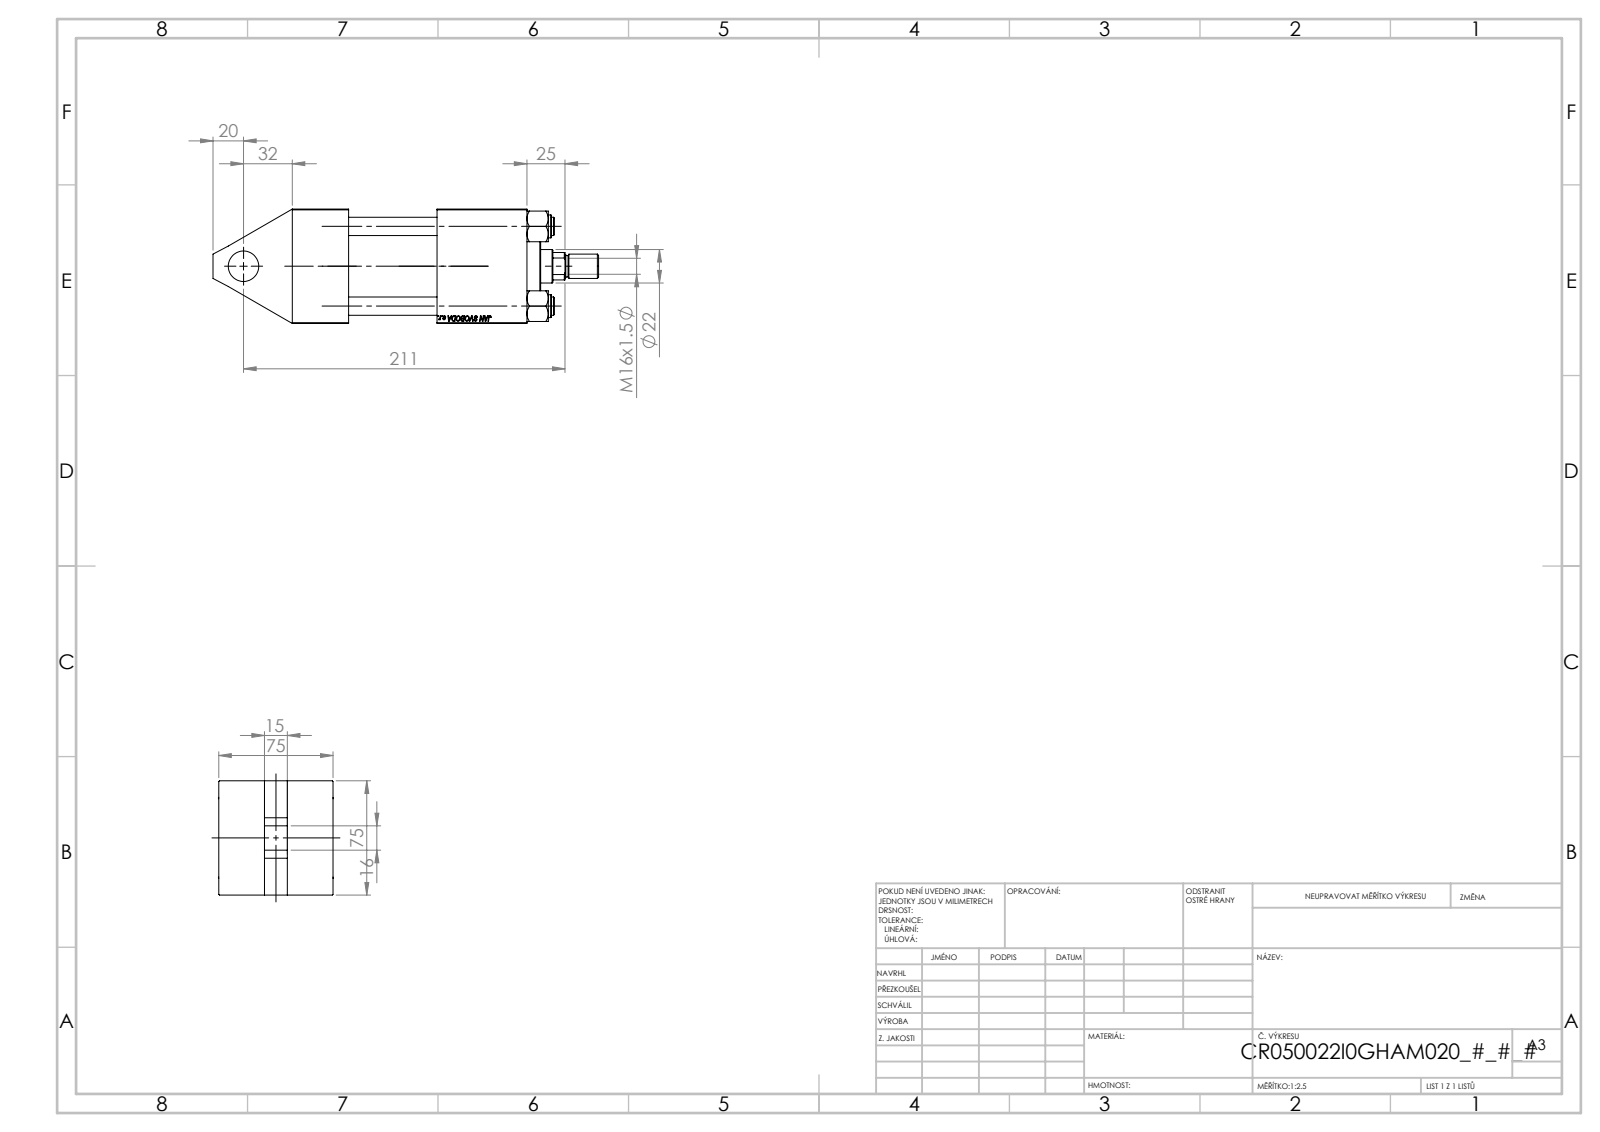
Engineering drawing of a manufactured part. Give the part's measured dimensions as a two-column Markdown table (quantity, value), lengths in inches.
| quantity | value |
| --- | --- |
| part name | V215CR_VCP_I; ROD_END_AH; V215CR_TYCINKA_I; NUT_M5_I (+2 more) |
| STEP written by | SolidWorks 2019 (CONFIG_CONTROL_DESIGN) |
| units | inches |
| bodies | 12 solids, 1093 faces (506 planar, 85 cylindrical, 502 other) |
| overall size | 9.961 × 2.974 × 2.953 |
| volume | 42.95 in³ |
| surface area | 244.6 in² |
| round holes (diameter × count) | 0.472 × 4, 0.276 × 2, 0.825 × 2, 1.181 × 2, 0.413 × 1, 0.787 × 1, 0.866 × 1, 0.984 × 1, 1.614 × 1, 1.969 × 1, 2.087 × 1 |
| round bosses / shafts (diameter × count) | 0.591 × 4, 2.205 × 1, 1.339 × 1, 0.63 × 1, 0.551 × 1 |
| partial cylindrical surfaces (radius × count) | 0.413 × 1 |
| main face-to-face distances | 2.953, 4.606, 1.457, 6.063, 1.181, 1.772, 3.74, 2.283, 2.323, 4.933 |
| hole center spacings | 1.456, 2.059, 2.912, 1.988, 3.681, 5.669 |
